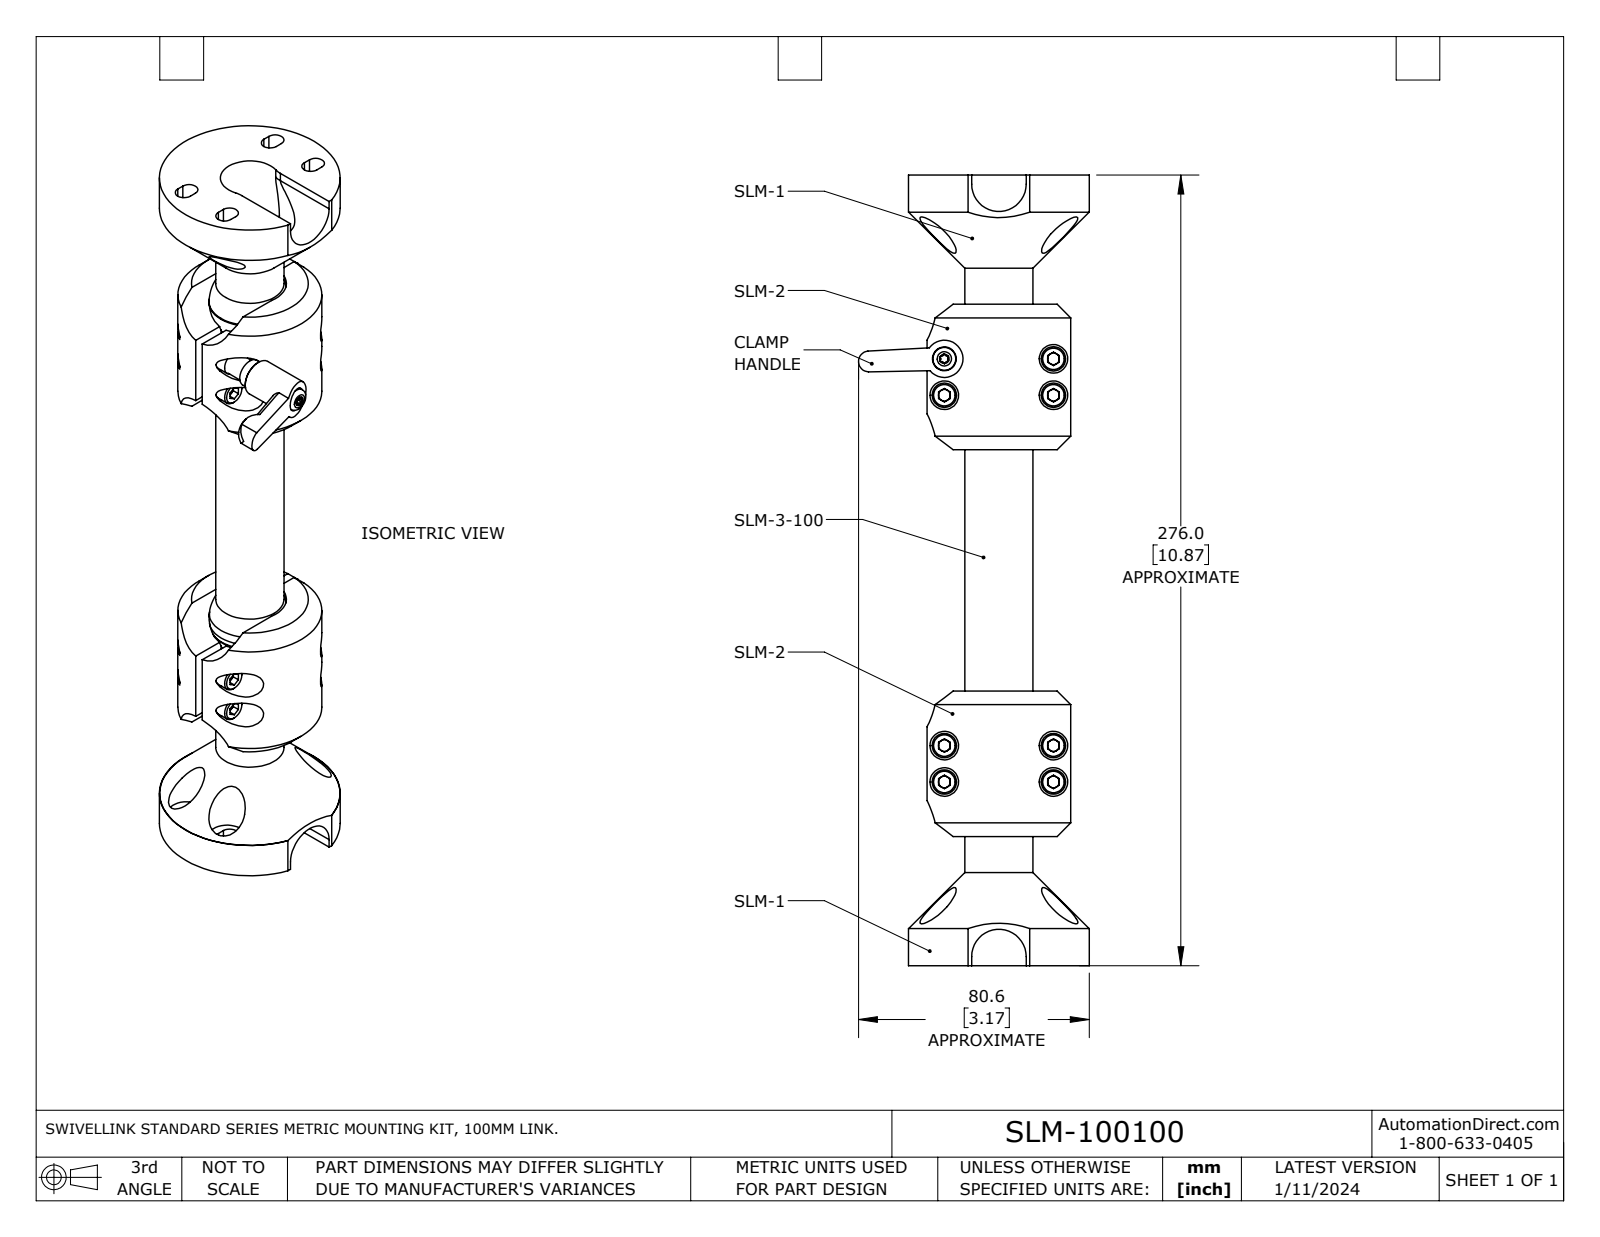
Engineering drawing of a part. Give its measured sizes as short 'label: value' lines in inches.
name: SLM-100100
written by: SolidWorks 2023 (AUTOMOTIVE_DESIGN)
unit: in
bodies: 17 solids, 421 faces (203 planar, 124 cylindrical, 94 other)
size: 10.866 × 3.216 × 3.173
volume: 15.49 in³; area: 143.7 in²
holes: 8× ⌀0.165, 8× ⌀0.228, 8× ⌀0.394, 4× ⌀0.5, 1× ⌀0.097, 1× ⌀0.192, 1× ⌀0.327, 1× ⌀0.75, 1× ⌀0.813, 1× ⌀1
bosses: 8× ⌀0.335, 8× ⌀0.197, 1× ⌀2.485, 1× ⌀1.98, 1× ⌀1.115, 1× ⌀1.115, 1× ⌀0.937, 1× ⌀0.512
rounds: 8× R0.121, 6× R0.013, 6× R0.023, 4× R0.375, 4× R0.497, 1× R0.143, 1× R0.165
face distances: 10.867, 0.125, 2, 5.315, 0.313, 0.187, 0.413, 10.454, 9.091, 1.776
hole spacings: 0.5, 0.925, 1.5, 1.581, 5.315, 5.522, 0.787, 1.673
